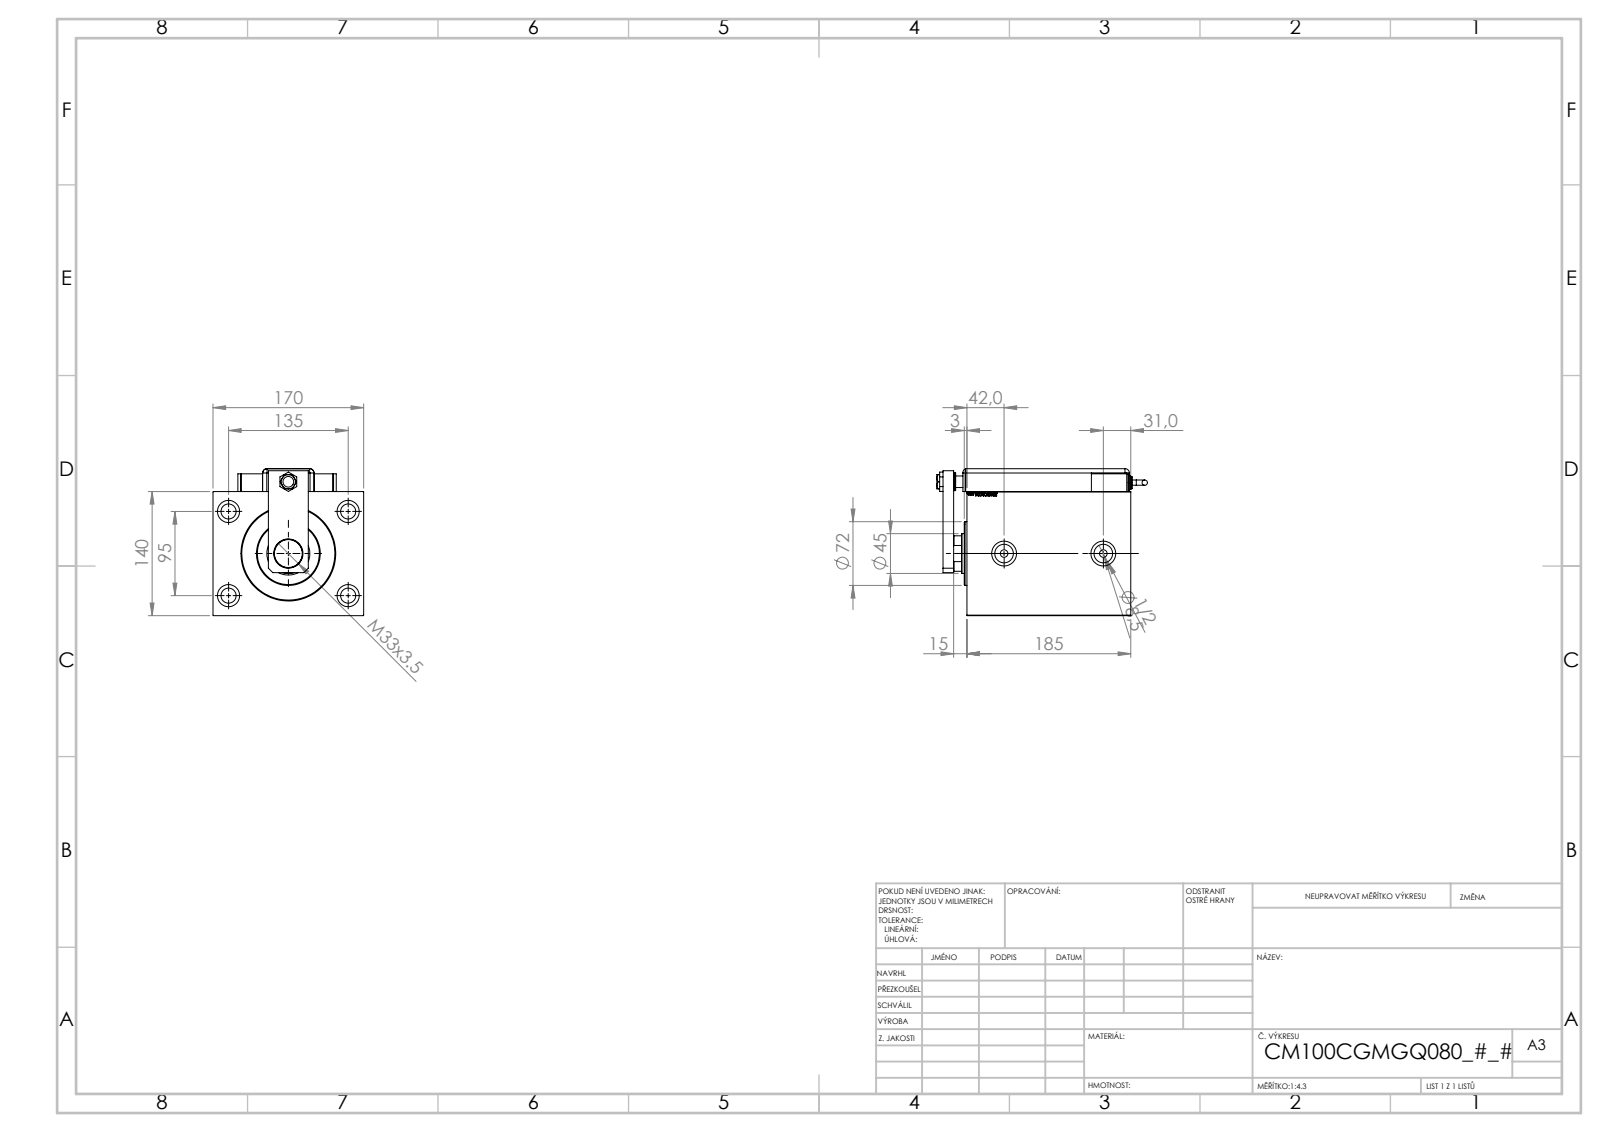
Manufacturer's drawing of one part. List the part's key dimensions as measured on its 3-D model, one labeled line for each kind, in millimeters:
Part name (STEP PRODUCT): MAGNETIC SWITCH Q; KRYT; ZARAZKA_Q; V450CM_C_VCP (+7 more)
STEP written by: SolidWorks 2019 (CONFIG_CONTROL_DESIGN)
Units: millimetres
Bodies: 13 solids, 1249 faces (615 planar, 117 cylindrical, 517 other)
Overall size (bounding box): 237.66 × 170 × 165.8
Volume: 3 900 000 mm³ · Surface area: 416 513 mm²
Round holes (diameter × count): ⌀17 ×4, ⌀25 ×4, ⌀4 ×2, ⌀8 ×2, ⌀8.5 ×2, ⌀20.96 ×2, ⌀28 ×2, ⌀12 ×1, ⌀13 ×1, ⌀14 ×1, ⌀31.5 ×1, ⌀33 ×1
Round bosses / shafts (diameter × count): ⌀20 ×3, ⌀16 ×2, ⌀14 ×2, ⌀6 ×2, ⌀72 ×1
Partial cylindrical surfaces — rounded edges, fillets, slot ends (radius × count): R5 ×9, R10 ×1, R22 ×1
Main face-to-face distances: 170, 140, 185, 3, 26, 159, 15, 25.8, 165.8, 1.5
Hole centre spacings: 82.54, 75.36, 95, 135, 145.15, 165.08, 20, 81
